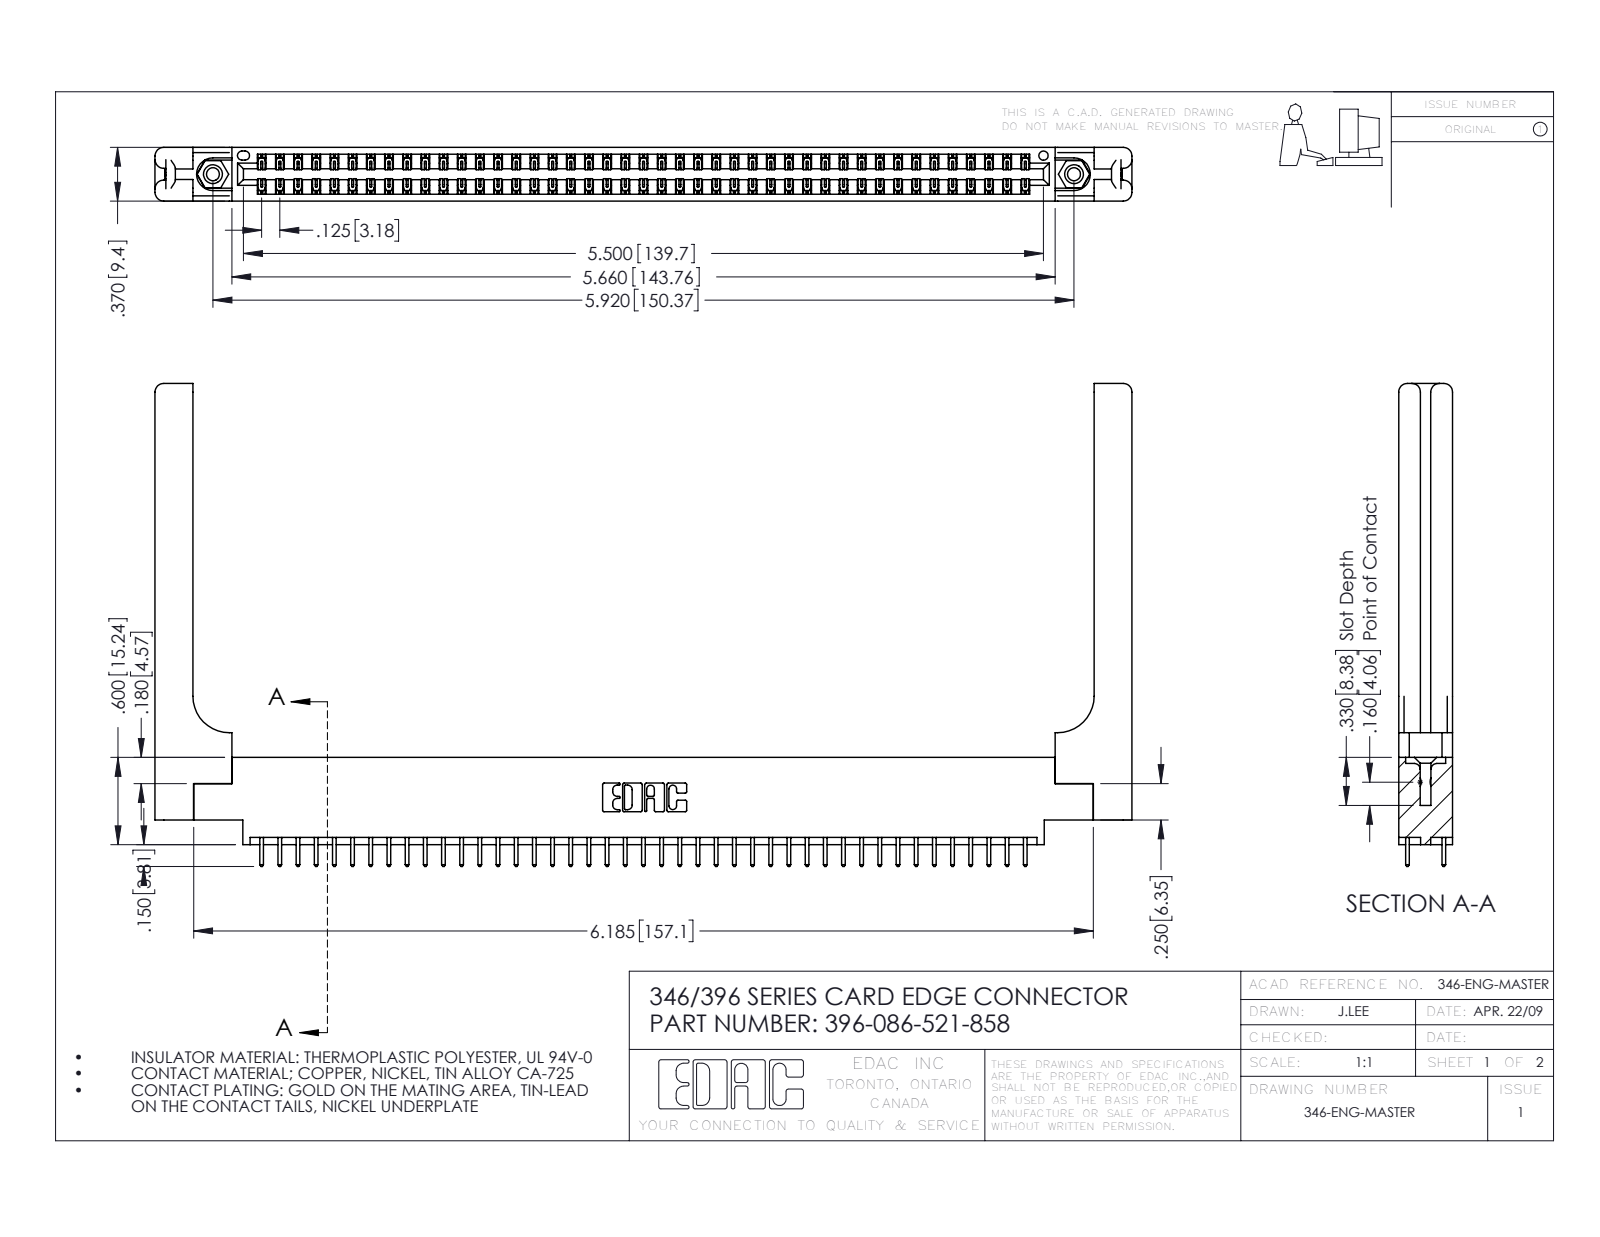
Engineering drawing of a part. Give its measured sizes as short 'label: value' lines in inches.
name: 345-250-001_345-250-001-102; 396-086-521-858; 346-220-058_345-220-058; 345-292-001_345-293-121 (+1 more)
written by: SolidWorks 2016 (CONFIG_CONTROL_DESIGN)
unit: in
bodies: 91 solids, 4854 faces (3238 planar, 1556 cylindrical, 60 other)
size: 6.716 × 3.32 × 0.37
volume: 1.461 in³; area: 42.7 in²
holes: 2× ⌀0.089, 2× ⌀0.125, 2× ⌀0.156, 1× ⌀0.064
bosses: 2× ⌀0.155
rounds: 129× R0.006, 86× R0.01, 22× R0.01, 16× R0.06, 6× R0.007, 6× R0.031, 3× R0.026, 2× R0.014
face distances: 0.37, 0.048, 0.322, 0.072, 0.148, 0.15, 0.25, 0.025, 0.298, 0.275
hole spacings: 0.246, 5.711, 5.92
